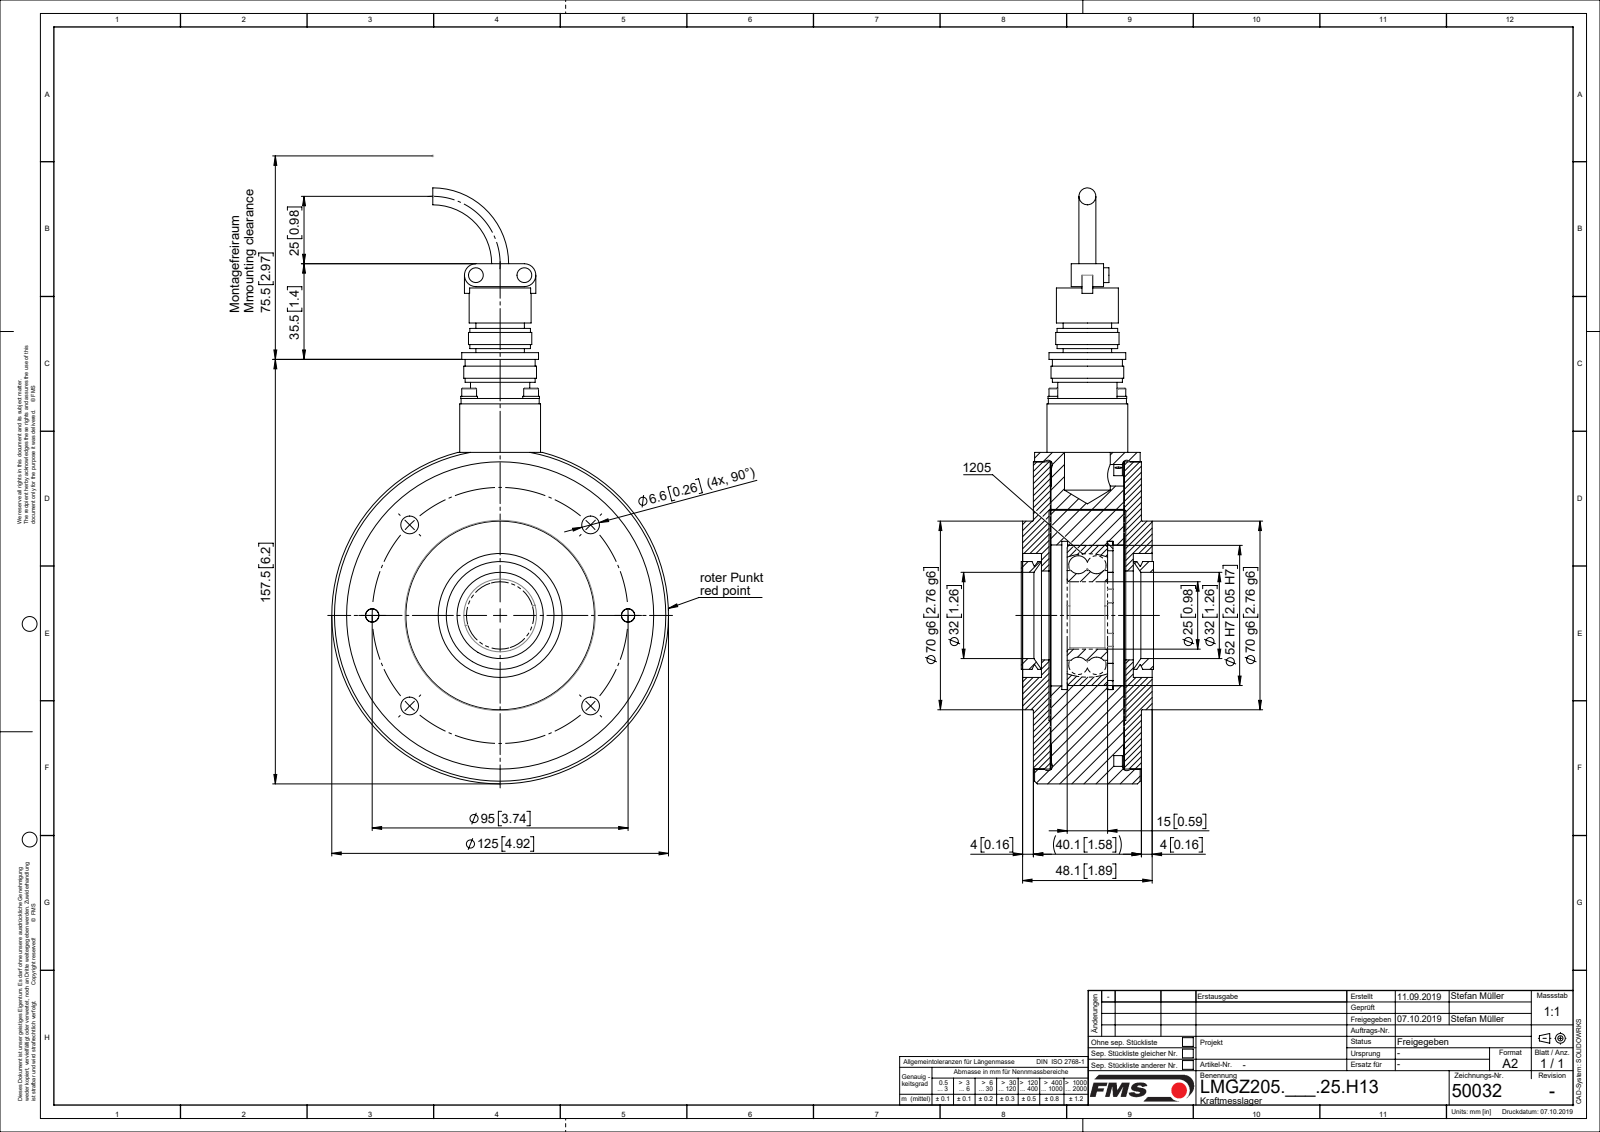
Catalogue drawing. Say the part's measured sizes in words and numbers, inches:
The part is named "L50032; L4832404; L48964; TEIL1 (+8 more)". Its 3-D file was written by "Mechanical Desktop 2007 (CONFIG_CONTROL_DESIGN)". It is 21 solids with 424 faces: 112 planar, 252 cylindrical and 60 other. Overall it measures 8.707 by 4.921 by 1.894 inches. Its volume is 29.5 cubic inches and its surface area 225.8 square inches. Round holes: 6 of diameter 0.26, 4 of diameter 0.102, 4 of diameter 0.126, 4 of diameter 0.134, 2 of diameter 0.197, 2 of diameter 0.433, 1 of diameter 0.906, 1 of diameter 0.984, 1 of diameter 1.22, 1 of diameter 1.299, 1 of diameter 1.492, 1 of diameter 1.811. Round bosses or shafts: 6 of diameter 0.217, 4 of diameter 0.244, 4 of diameter 0.118, 4 of diameter 0.098, 2 of diameter 0.394, 2 of diameter 0.236, 1 of diameter 4.921, 1 of diameter 4.488. Partial cylindrical surfaces (rounded edges, fillets, slot ends): 8 of radius 0.197, 2 of radius 0.167, 1 of radius 1.594, 1 of radius 1.85. The main face-to-face distances are 1.073, 1.321, 0.248, 0.258, 1.331, 1.063, 1.083, 0.157, 0.415, 1.579. The hole center spacings are 1.87, 0.64, 0.906, 1.431, 2.645, 3.456, 1.281, 3.741.
